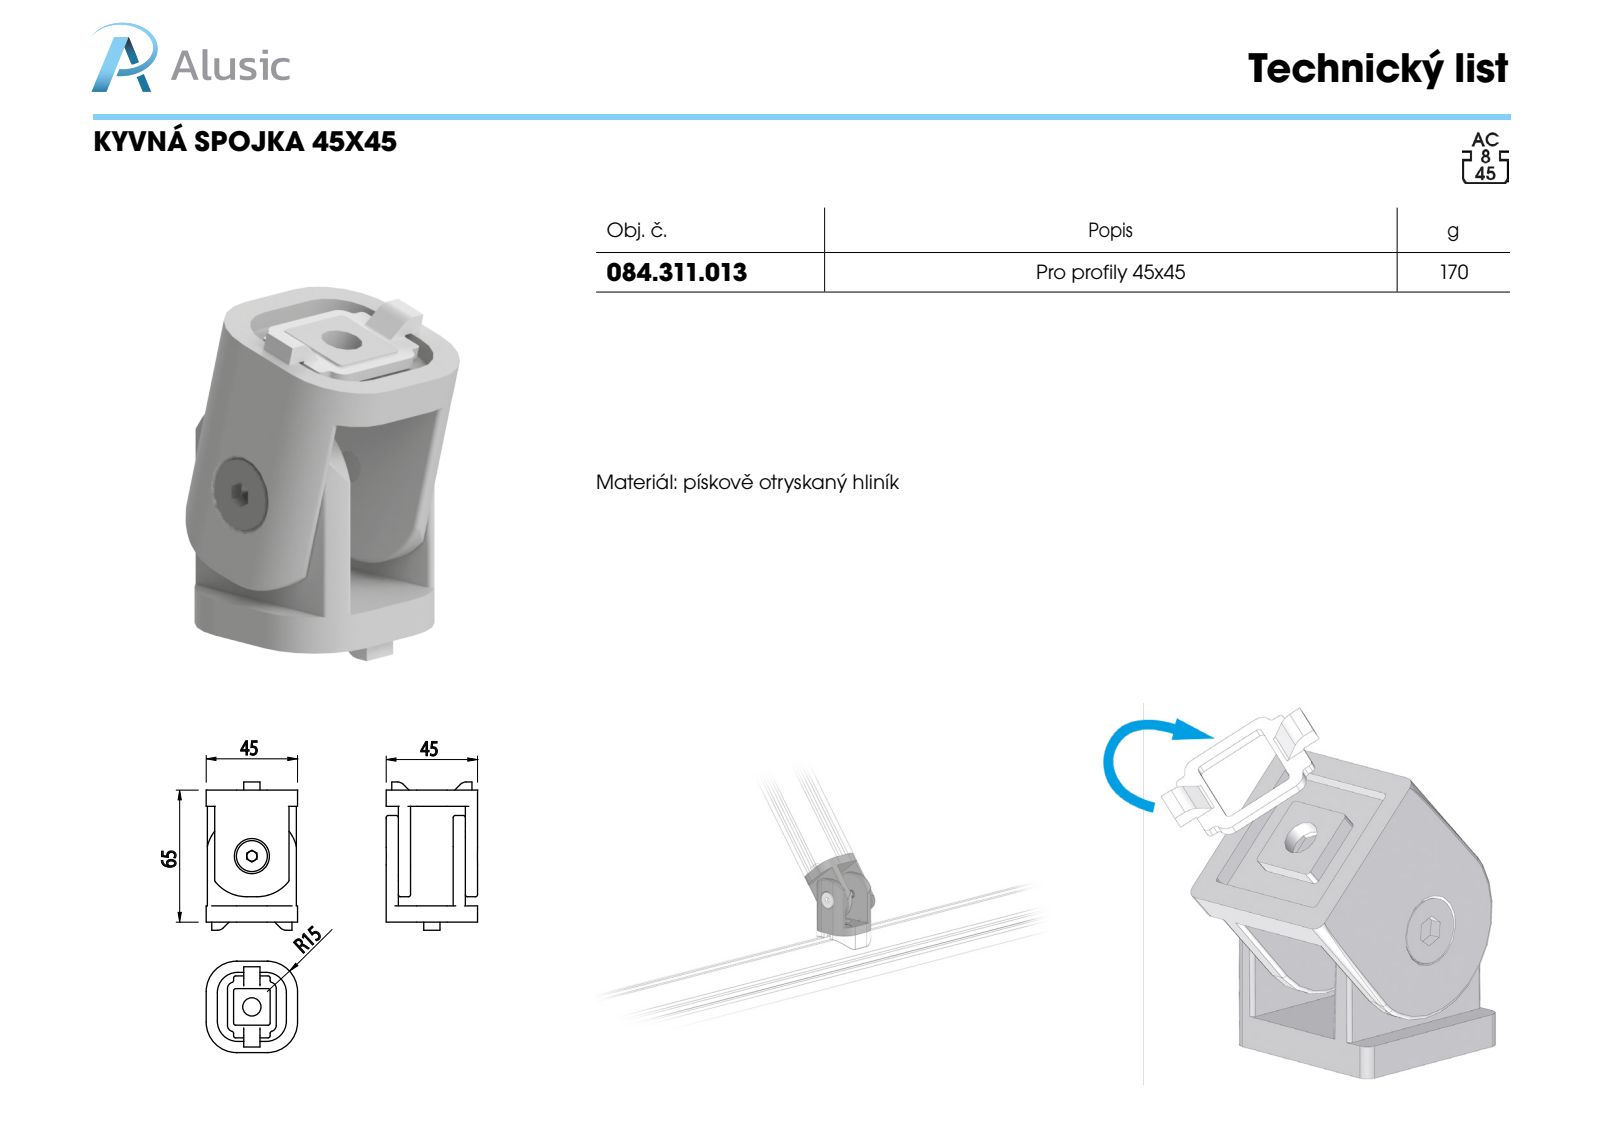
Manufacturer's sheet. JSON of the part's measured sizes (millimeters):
{"part_name": "084.311.013; 084.311.010-2; socket countersunk head screw_iso_ISO 10642 - M8 x 16 --- 16S; 084.311.013-1", "step_written_by": "SolidWorks 2012 (CONFIG_CONTROL_DESIGN)", "units": "millimeters", "bodies": {"solids": 6, "faces": 392, "planar": 140, "cylindrical": 140, "other": 112}, "overall_size": [75.55, 56.91, 45], "volume_mm3": 61625, "surface_area_mm2": 30780, "round_holes": [[9, 3], [6.8, 1]], "round_bosses_or_shafts": [[15.24, 1], [8, 1]], "partial_cylinders_radius": [[1, 50], [3, 8], [10, 8], [15, 8], [4, 4], [20, 4]], "face_to_face_distances": [6, 33, 27, 4, 21, 8, 12, 39, 7.99, 45]}
